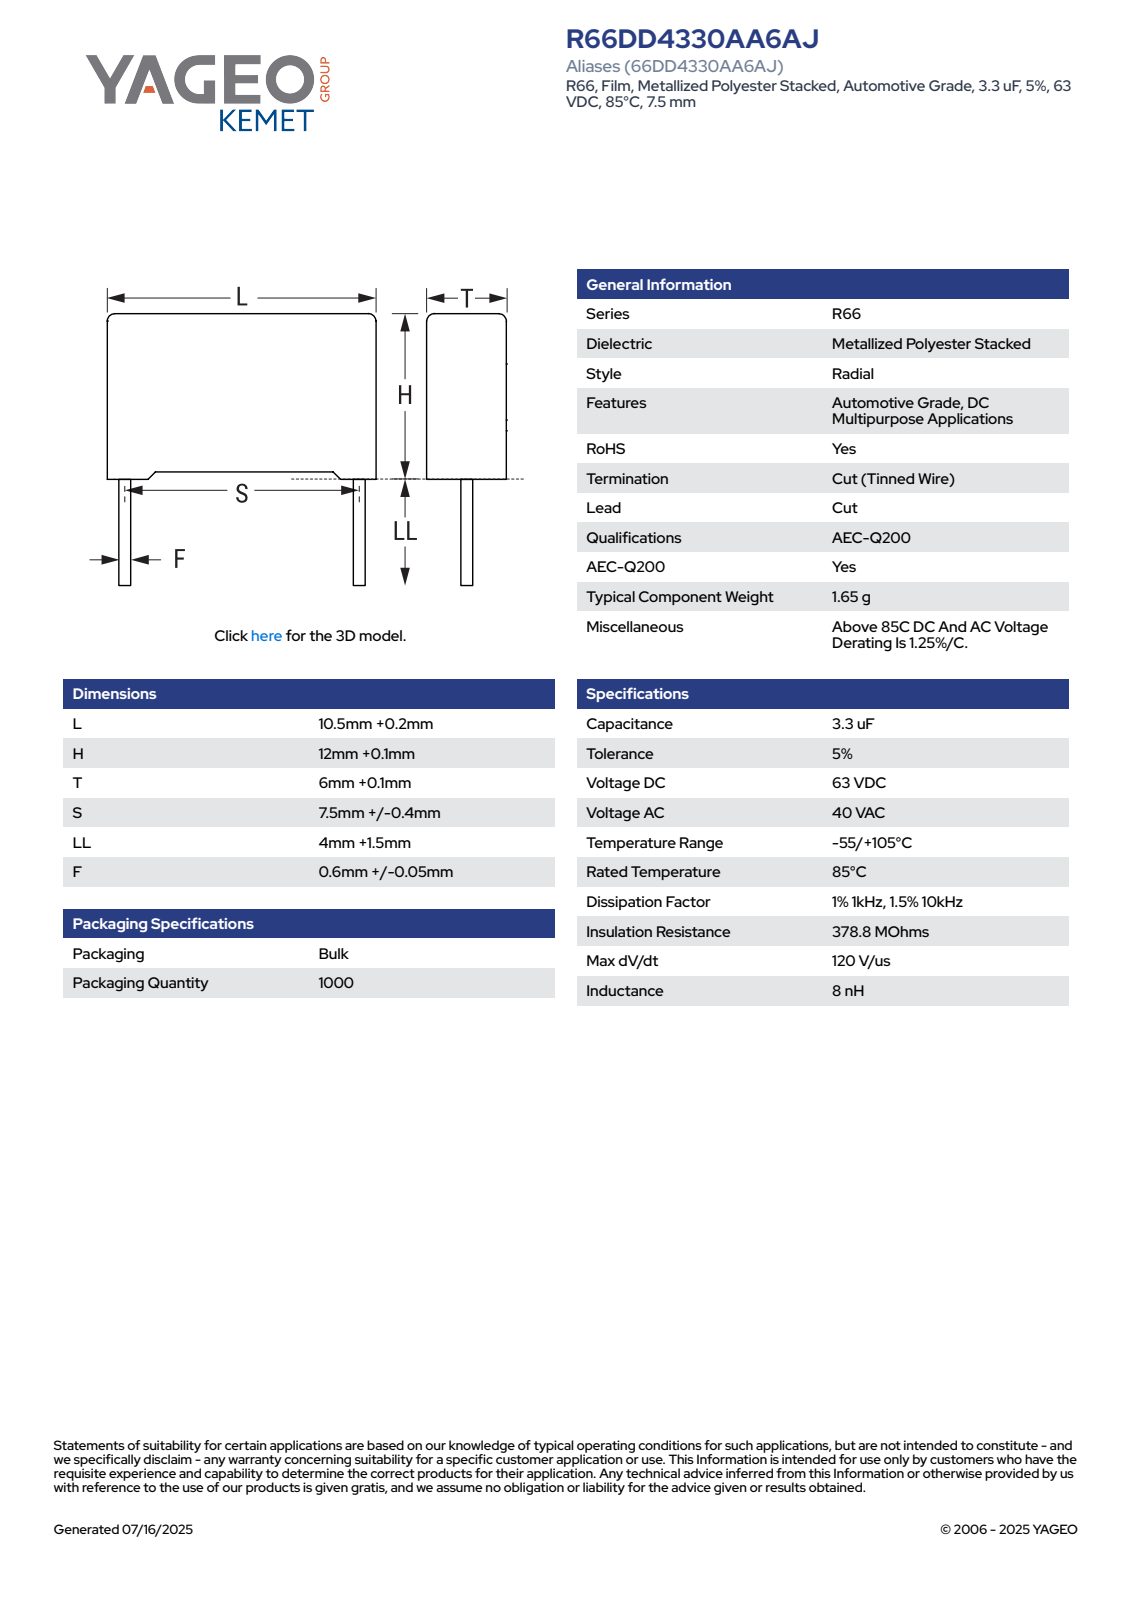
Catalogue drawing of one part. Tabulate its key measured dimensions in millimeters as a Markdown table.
| quantity | value |
| --- | --- |
| part name | CFR_RB2_10.5X12X6_L10.7H12.1T6.1S7.5LL5.5F0.65 |
| STEP written by | SolidWorks 2021 (AUTOMOTIVE_DESIGN) |
| units | millimeters |
| bodies | 4 solids, 85 faces (77 planar, 8 cylindrical, 0 other) |
| overall size | 17.6 × 10.7 × 6.11 |
| volume | 751 mm³ |
| surface area | 580 mm² |
| round bosses / shafts (diameter × count) | 0.65 × 2 |
| partial cylindrical surfaces (radius × count) | 0.5 × 4 |
| main face-to-face distances | 6.1, 10.7, 11.35, 0.36, 5.74, 0.75, 12.1, 10.34, 5.38, 9.98 |
